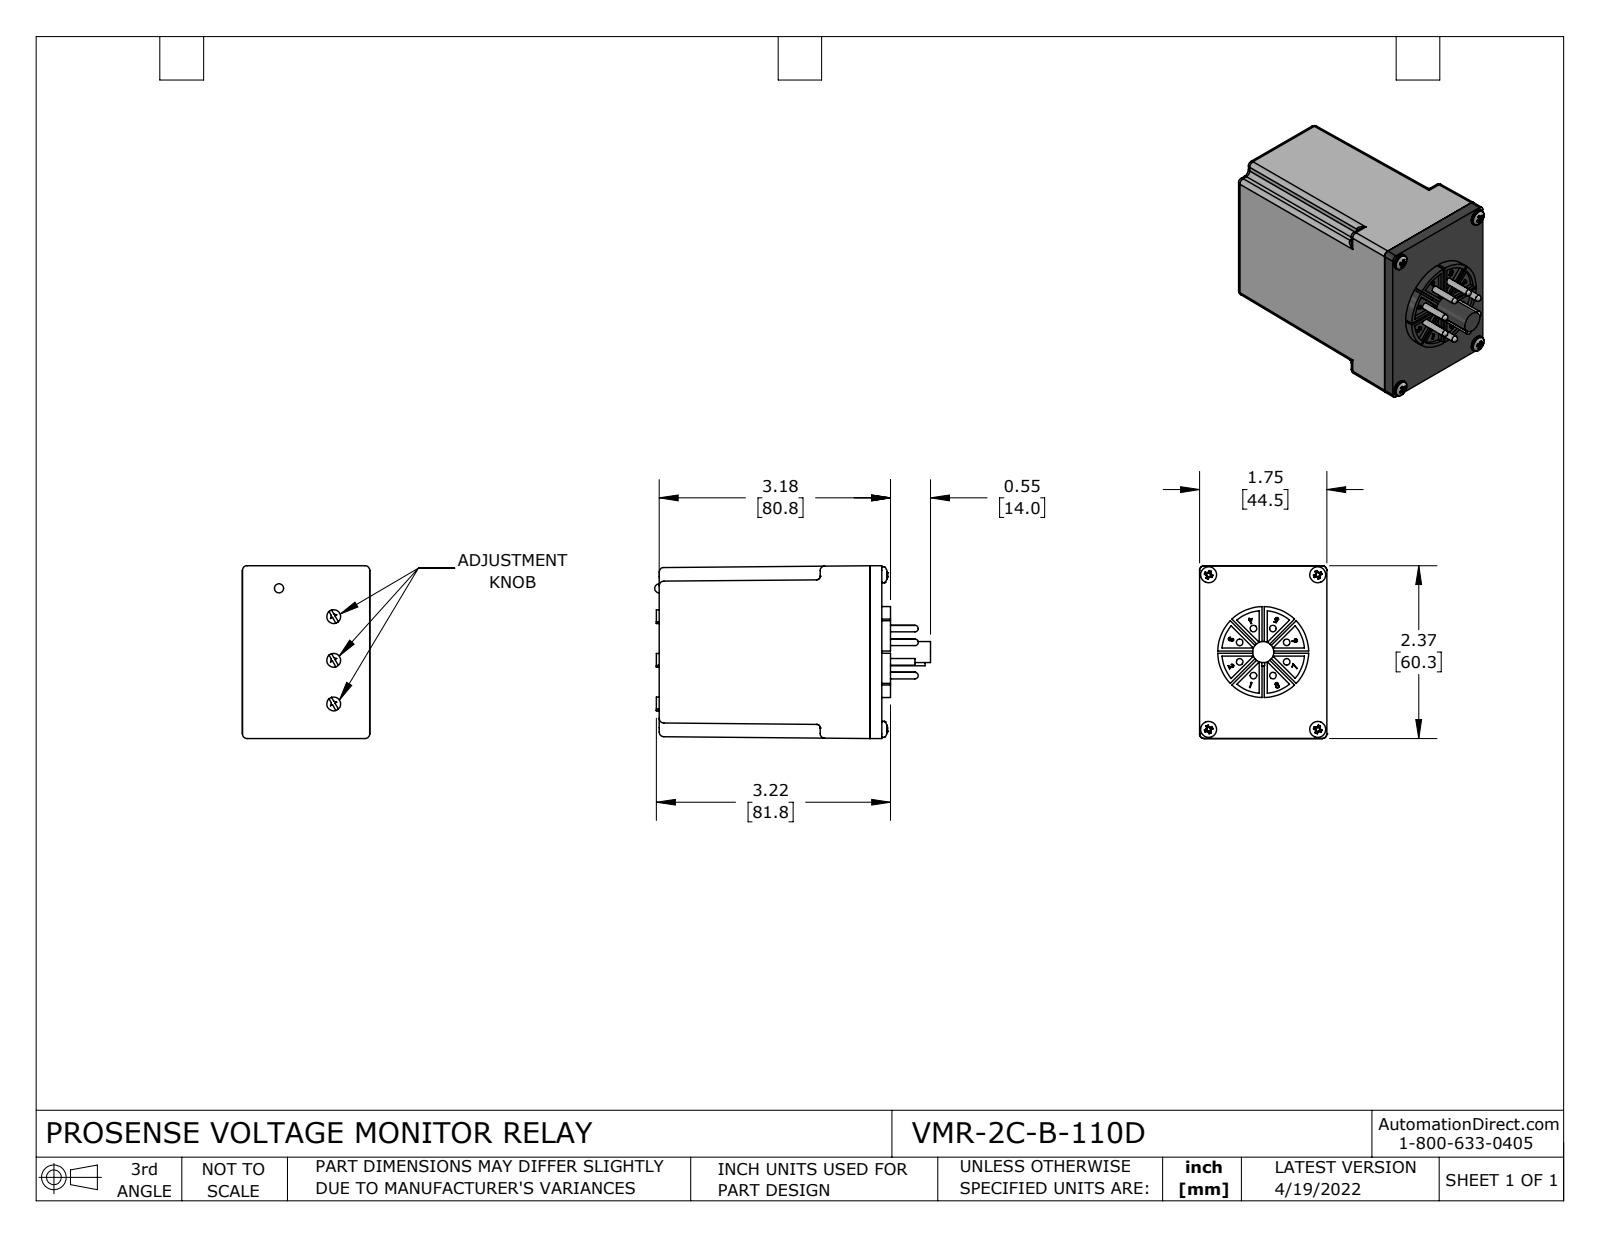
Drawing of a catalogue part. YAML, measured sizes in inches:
part_name: "VMR-2C-B-110D"
step_written_by: "SolidWorks 2021 (CONFIG_CONTROL_DESIGN)"
units: inches
bodies: {solids: 18, faces: 574, planar: 249, cylindrical: 170, other: 155}
overall_size: [3.79, 2.375, 1.75]
volume: 12.25
surface_area: 44.71
round_holes:
  - {diameter: 0.125, count: 4}
round_bosses_or_shafts:
  - {diameter: 0.09, count: 8}
  - {diameter: 0.219, count: 4}
  - {diameter: 0.19, count: 3}
  - {diameter: 1.25, count: 1}
  - {diameter: 0.29, count: 1}
partial_cylinders:
  - {radius: 0.063, count: 32}
  - {radius: 0.005, count: 8}
  - {radius: 0.05, count: 4}
  - {radius: 0.57, count: 1}
face_to_face_distances: [2.9, 0.16, 3.06, 0.07, 0.23, 3.13, 0.188, 0.05, 0.12, 0.28]
hole_center_spacings: [1.5, 2.125, 2.601]
